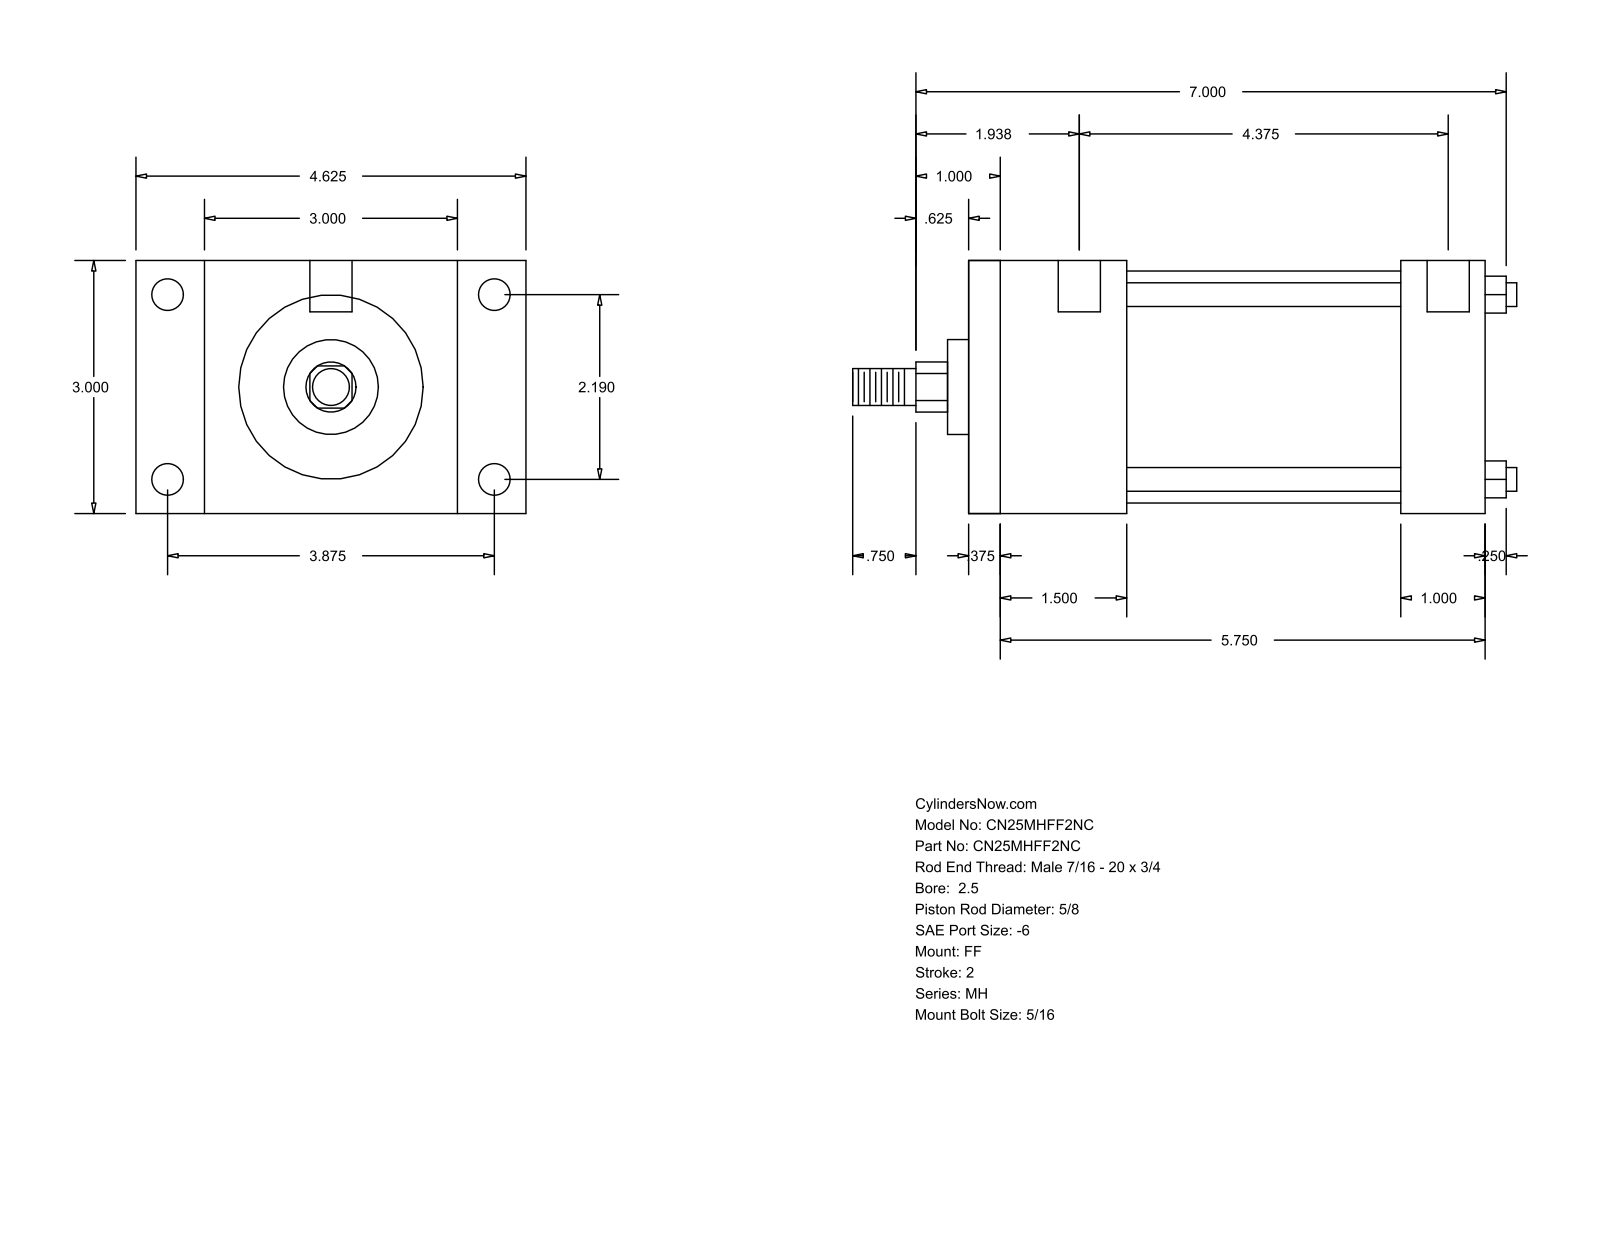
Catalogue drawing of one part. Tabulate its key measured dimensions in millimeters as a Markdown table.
| quantity | value |
| --- | --- |
| part name | MH_FF__0250_0.625 |
| STEP written by | GSSL Pune (CONFIG_CONTROL_DESIGN) |
| units | millimeters |
| bodies | 0 solids, 92 faces (64 planar, 28 cylindrical, 0 other) |
| overall size | 200.03 × 117.47 × 76.2 |
| round holes (diameter × count) | 5.56 × 4, 9.53 × 4, 12.7 × 2 |
| round bosses / shafts (diameter × count) | 7.14 × 4, 69.85 × 1, 28.57 × 1, 15.88 × 1, 11.11 × 1 |
| partial cylindrical surfaces (radius × count) | 7.54 × 1 |
| main face-to-face distances | 76.2, 155.57, 9.52, 146.05, 25.4, 82.55, 47.62, 130.17, 38.1, 120.65 |
| hole center spacings | 55.62, 98.42, 113.05, 119.06, 3.17, 4.76, 111.13, 114.3 |
